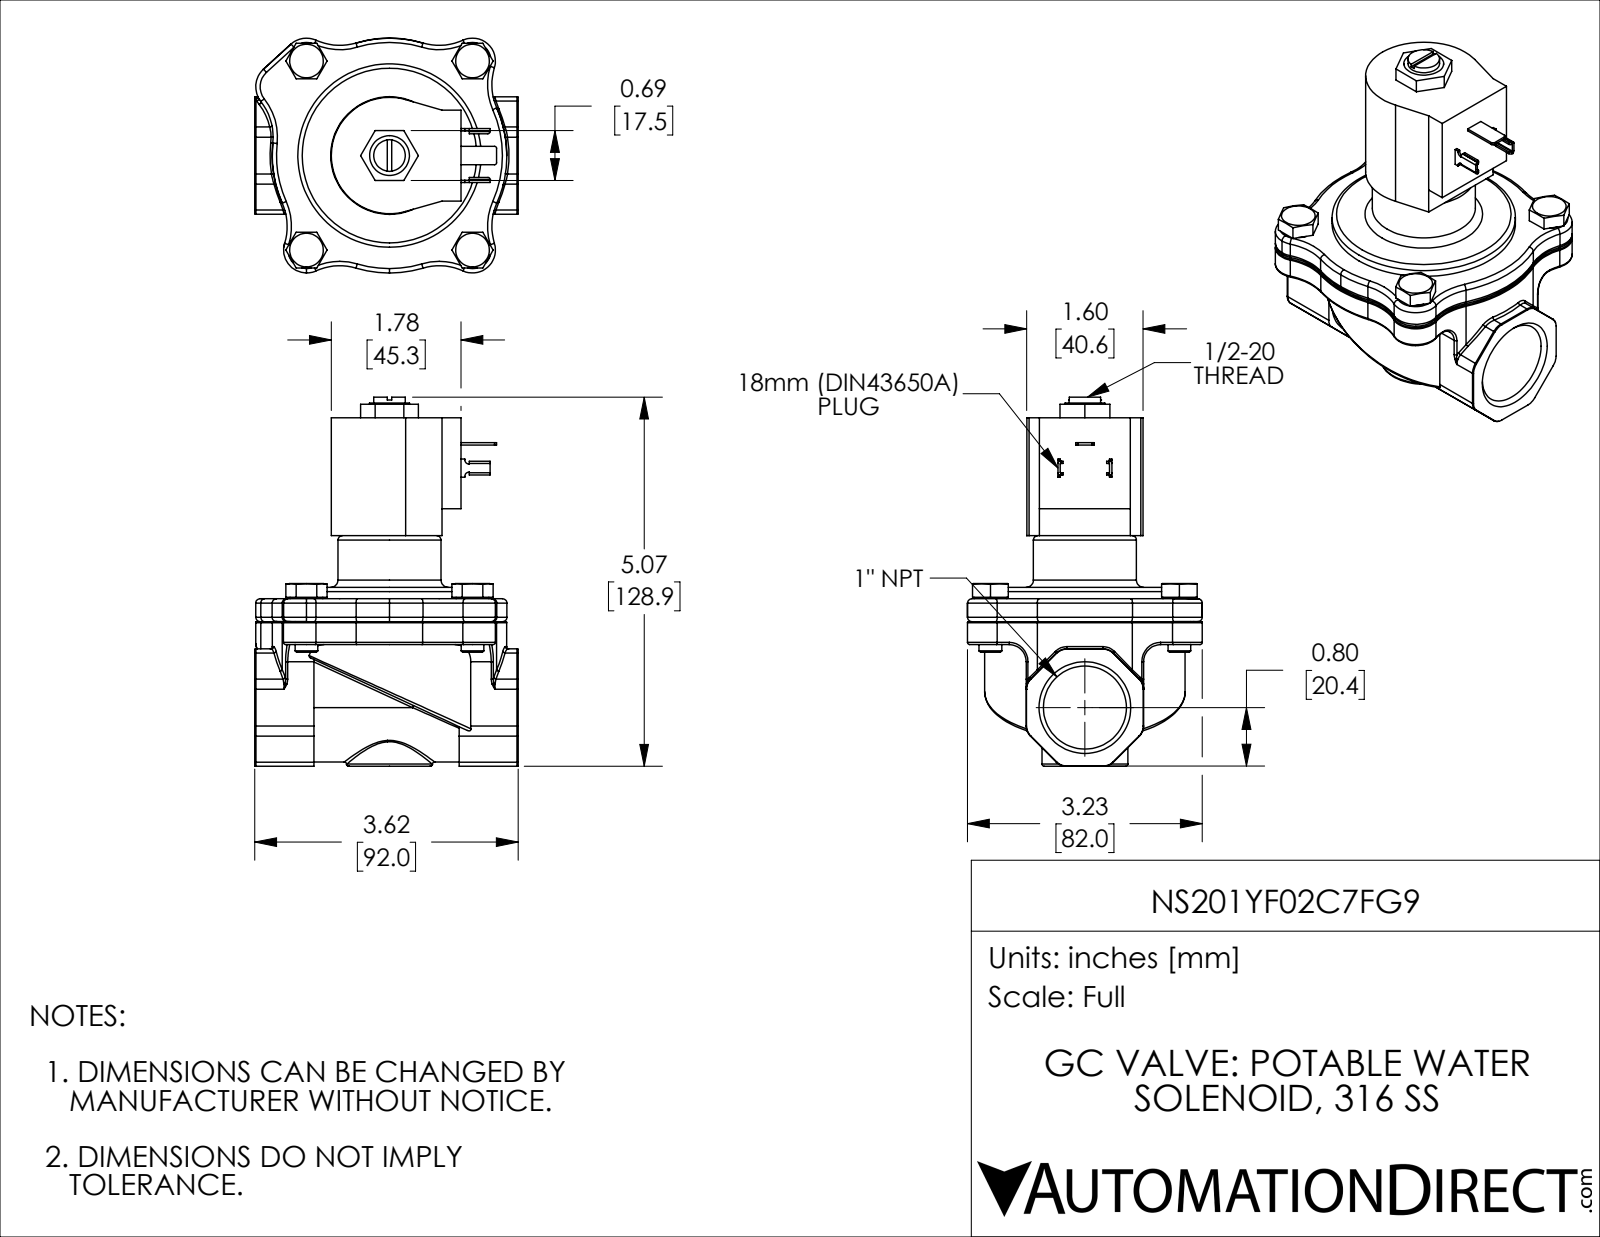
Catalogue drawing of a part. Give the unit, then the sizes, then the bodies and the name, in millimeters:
Units: millimetres
Overall size (bounding box): 128.9 × 92 × 82
Round holes (diameter × count): ⌀6.4 ×4, ⌀8 ×4, ⌀3.2 ×1, ⌀6 ×1, ⌀12.4 ×1, ⌀12.8 ×1, ⌀24.1 ×1, ⌀29 ×1, ⌀76.2 ×1
Round bosses / shafts (diameter × count): ⌀11.4 ×4, ⌀8 ×4, ⌀67.3 ×1, ⌀64 ×1, ⌀36 ×1, ⌀30 ×1, ⌀13.9 ×1, ⌀11 ×1
Partial cylindrical surfaces — rounded edges, fillets, slot ends (radius × count): R0.8 ×26, R20 ×16, R0.8 ×8, R5 ×8, R8 ×6, R1.5 ×2, R6 ×2, R8.3 ×1
Main face-to-face distances: 8, 0.8, 8.8, 71.9, 71.1, 63.1, 4, 30.8, 30, 22
Hole centre spacings: 66, 43.9, 58, 87.8, 43.9, 43.9, 57.8, 58
Volume: 306 300 mm³ · Surface area: 66 060 mm²
Bodies: 12 solids, 603 faces (162 planar, 221 cylindrical, 220 other)
Part name (STEP PRODUCT): NS201YF02C7FG9
STEP written by: SolidWorks 2018 (AUTOMOTIVE_DESIGN)
